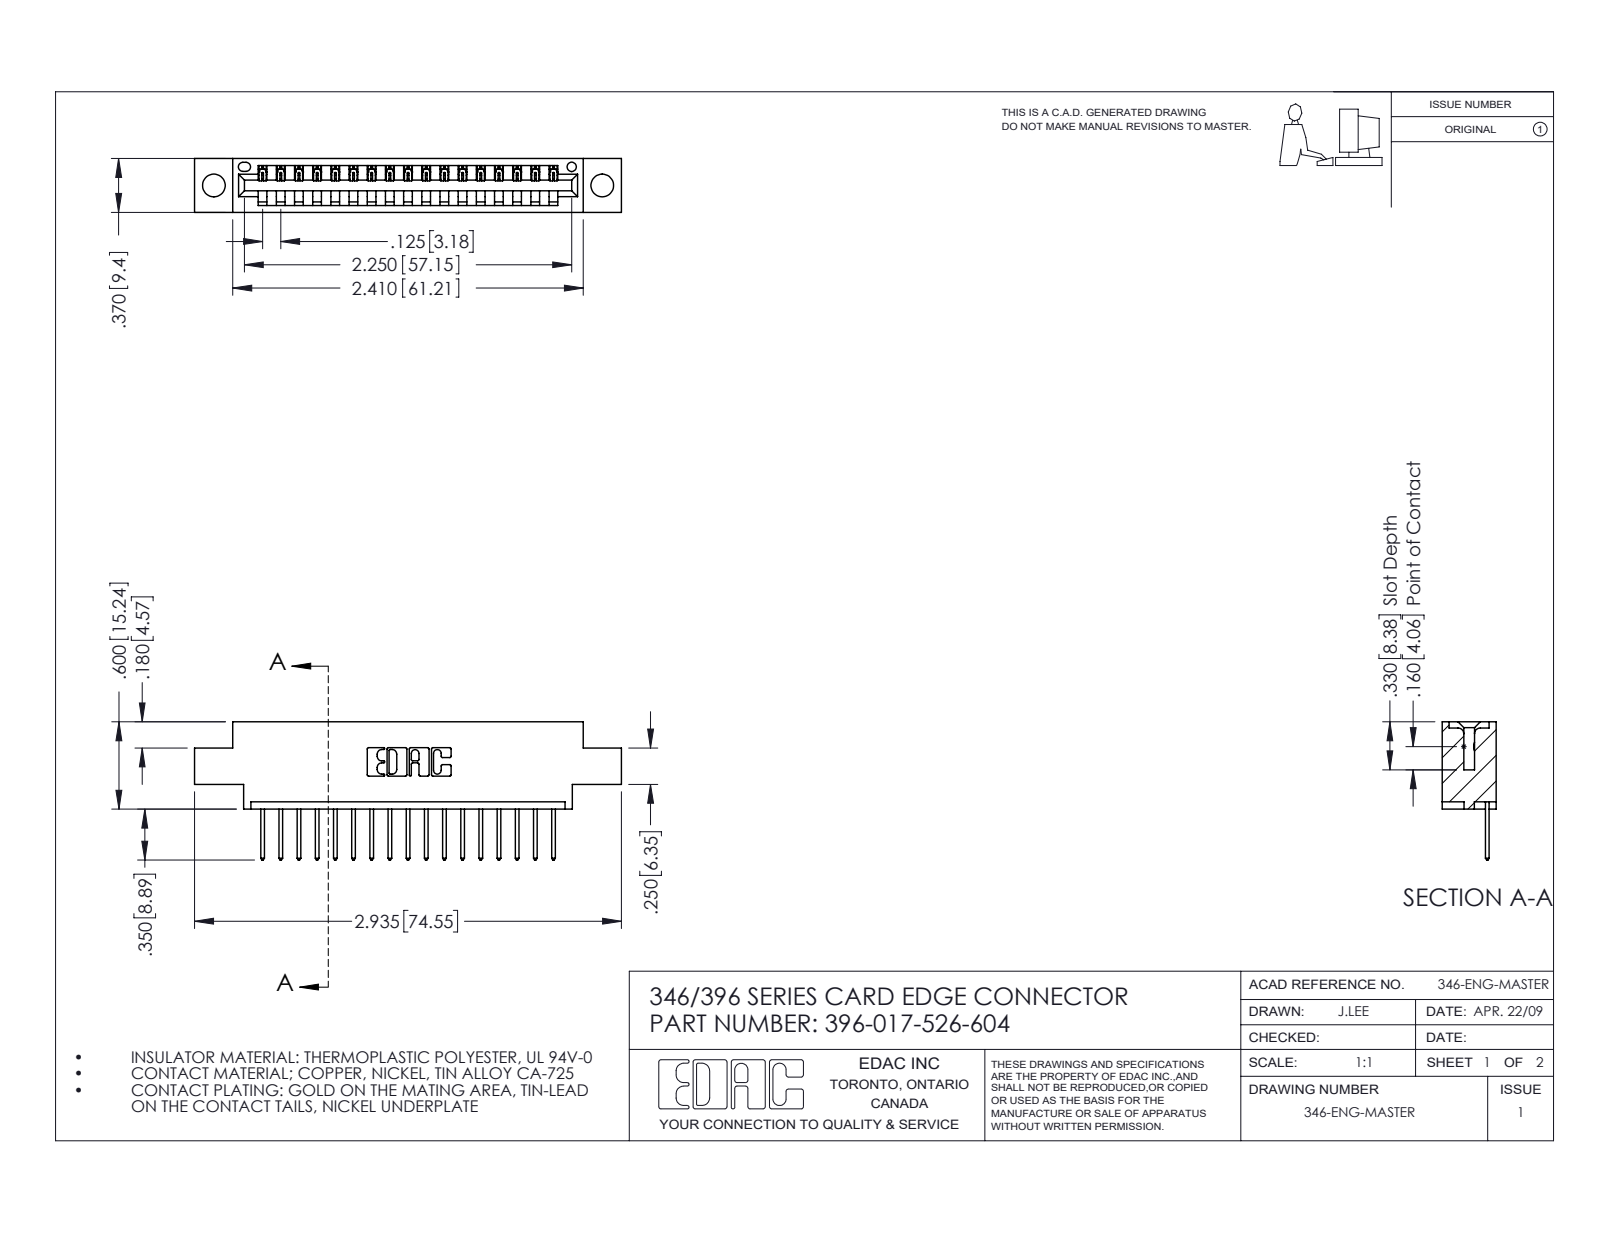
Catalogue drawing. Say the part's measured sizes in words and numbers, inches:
The part is named "346 Part_0.170 Offset - 0.156 Dia-TH; 345-292-001_345-293-126; 396-017-526-604". Its 3-D file was written by "SolidWorks 2016 (CONFIG_CONTROL_DESIGN)". It is 18 solids with 1112 faces: 760 planar, 352 cylindrical and 0 other. Overall it measures 2.935 by 0.95 by 0.37 inches. Its volume is 0.409 cubic inches and its surface area 12.5 square inches. Round holes: 2 of diameter 0.156, 1 of diameter 0.064. Partial cylindrical surfaces (rounded edges, fillets, slot ends): 34 of radius 0.006, 34 of radius 0.01, 22 of radius 0.01, 6 of radius 0.007, 6 of radius 0.031, 3 of radius 0.026, 2 of radius 0.031, 2 of radius 0.04. The main face-to-face distances are 0.048, 0.322, 0.37, 0.25, 0.072, 0.298, 0.025, 0.148, 0.222, 0.1. The hole center spacings are 0.246, 2.463, 2.67.
